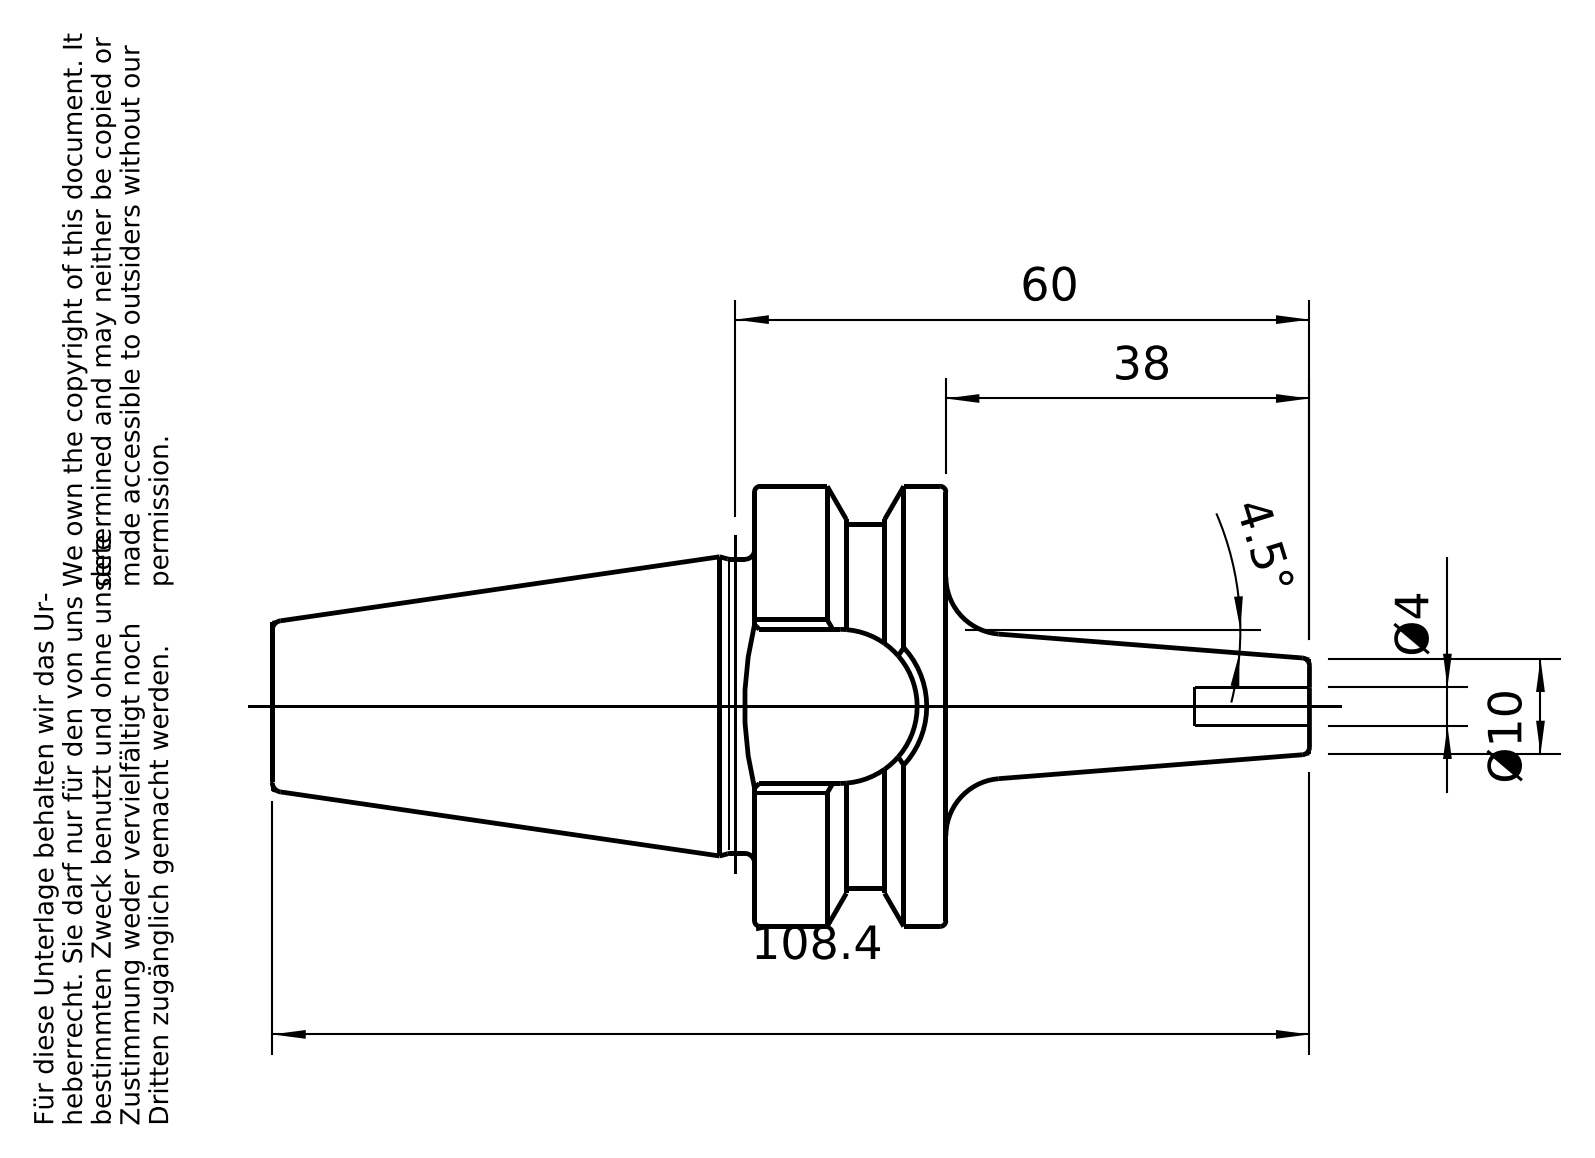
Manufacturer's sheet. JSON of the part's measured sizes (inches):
{"part_name": "30-645-04", "step_written_by": "PRO/ENGINEER BY PARAMETRIC TECHNOLOGY CORPORATION, 2010430 (CONFIG_CONTROL_DESIGN)", "units": "inches", "bodies": {"solids": 1, "faces": 94, "planar": 26, "cylindrical": 20, "other": 48}, "overall_size": [4.268, 1.81, 1.81], "volume_in3": 3.348, "surface_area_in2": 20.66, "round_holes": [[0.157, 1], [0.398, 1], [0.493, 1], [0.512, 1]], "round_bosses_or_shafts": [[1.81, 1], [1.211, 1], [0.473, 1]], "partial_cylinders_radius": [[0.319, 1], [0.743, 1]], "face_to_face_distances": [0.787, 1.272, 0.638, 1.984, 2.772, 4.268, 2.283, 1.496, 0.984, 1]}
